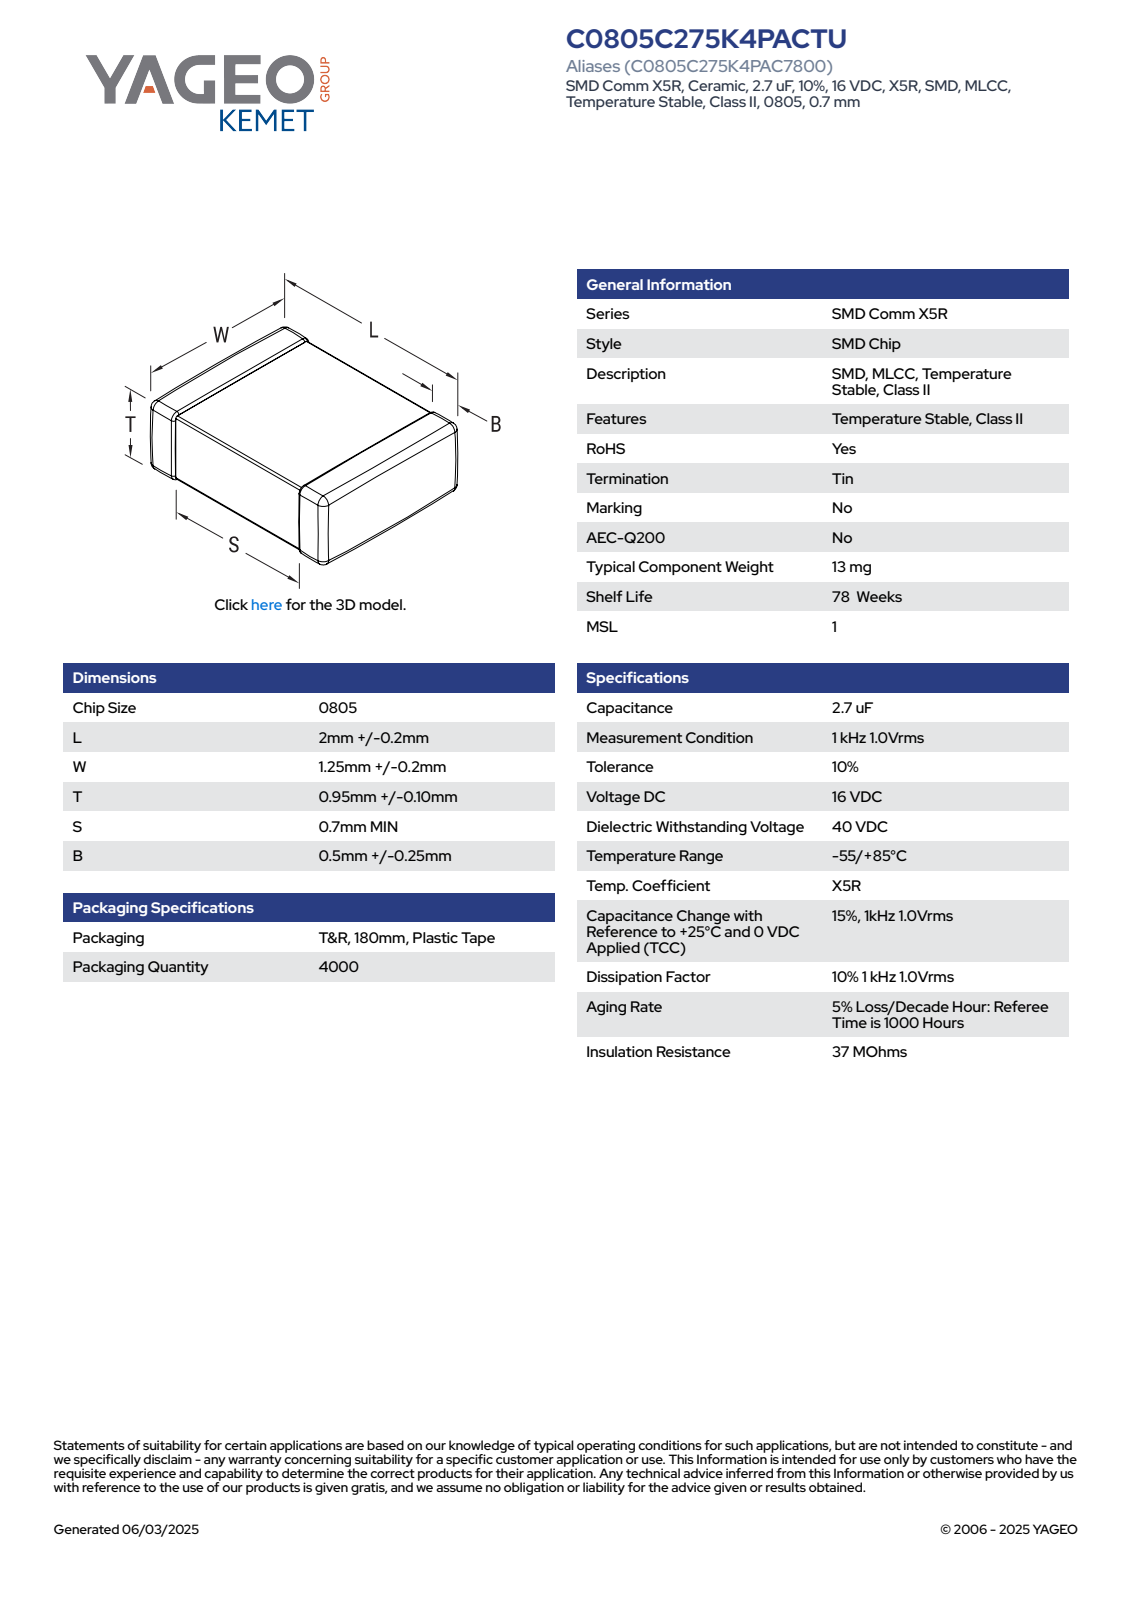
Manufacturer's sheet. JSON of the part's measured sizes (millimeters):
{"part_name": "CCS_CCSTD_0805_L2.2W1.45T1.05B0.5", "step_written_by": "SolidWorks 2021 (AUTOMOTIVE_DESIGN)", "units": "millimeters", "bodies": {"solids": 4, "faces": 125, "planar": 71, "cylindrical": 38, "other": 16}, "overall_size": [2.2, 1.45, 1.05], "volume_mm3": 3, "surface_area_mm2": 14, "face_to_face_distances": [1.02, 1.05, 2.2, 1.45, 1.42, 0.99, 1.39, 0.97, 1.23, 1.19]}
